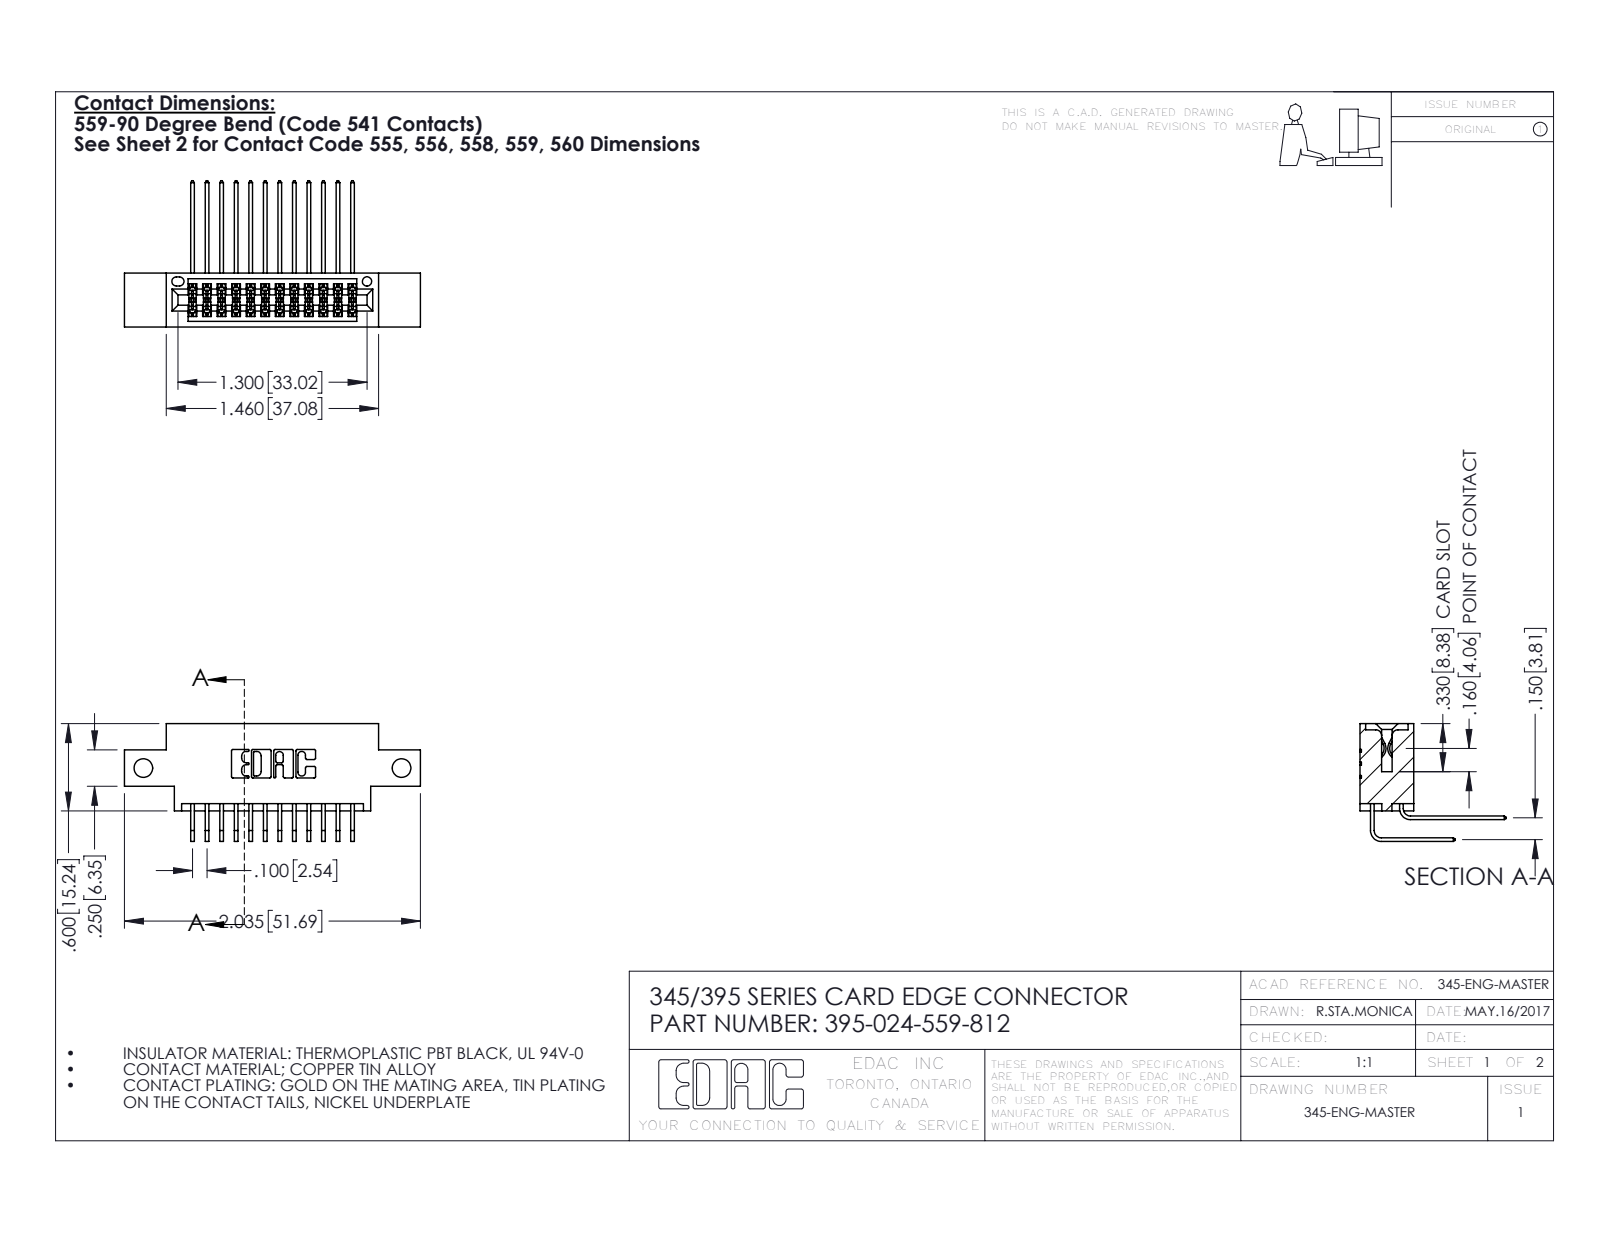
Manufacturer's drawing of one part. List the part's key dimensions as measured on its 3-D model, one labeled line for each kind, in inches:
Part name (STEP PRODUCT): 345-292-001_559 Tail - 2; 395-024-559-812; 345-292-001_558 559 Tail - 1; 345 Part_0.170 Offset - Side Mount
STEP written by: SolidWorks 2016 (CONFIG_CONTROL_DESIGN)
Units: inches
Bodies: 25 solids, 1378 faces (924 planar, 454 cylindrical, 0 other)
Overall size (bounding box): 2.035 × 1.005 × 0.809
Volume: 0.286 in³ · Surface area: 10.84 in²
Round holes (diameter × count): ⌀0.128 ×2, ⌀0.064 ×1
Partial cylindrical surfaces — rounded edges, fillets, slot ends (radius × count): R0.006 ×37, R0.01 ×22, R0.007 ×6, R0.031 ×6, R0.026 ×3, R0.014 ×2, R0.019 ×2, R0.022 ×2
Main face-to-face distances: 0.072, 0.298, 0.37, 0.2, 0.098, 0.272, 0.025, 0.15, 0.225, 0.175
Hole centre spacings: 1.775
